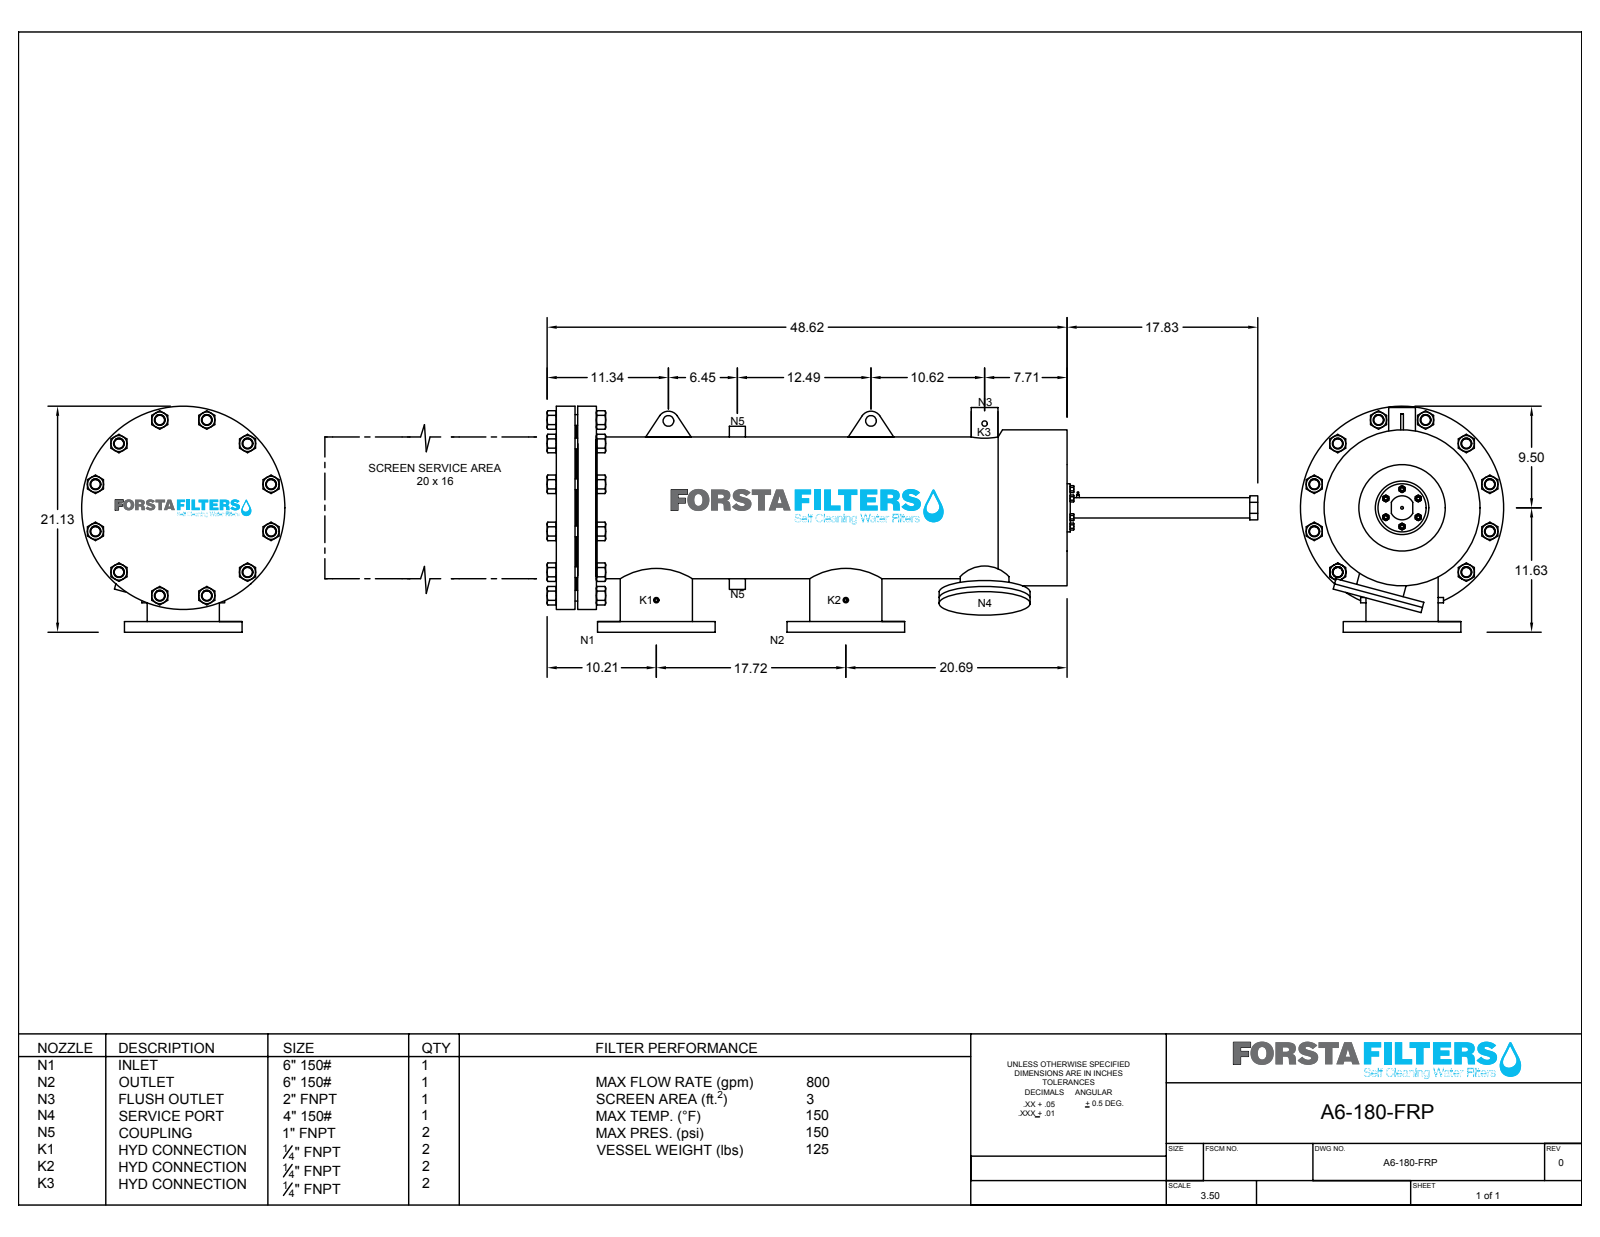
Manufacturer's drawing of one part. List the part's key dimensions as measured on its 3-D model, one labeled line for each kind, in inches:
Part name (STEP PRODUCT): A6-FRP-180
STEP written by: SolidWorks 2018 (CONFIG_CONTROL_DESIGN)
Units: inches
Bodies: 33 solids, 638 faces (306 planar, 328 cylindrical, 4 other)
Overall size (bounding box): 67.113 × 21.13 × 19
Volume: 1 571 in³ · Surface area: 7 748 in²
Round holes (diameter × count): ⌀0.75 ×16, ⌀0.88 ×16, ⌀1 ×15, ⌀0.25 ×4, ⌀0.375 ×4, ⌀0.375 ×2, ⌀4.106 ×2, ⌀5.996 ×2, ⌀1.51 ×1, ⌀2 ×1, ⌀12.858 ×1, ⌀14.187 ×1
Round bosses / shafts (diameter × count): ⌀0.35 ×6, ⌀0.644 ×3, ⌀11 ×2, ⌀9 ×2, ⌀6.39 ×2, ⌀4.5 ×2, ⌀19 ×1, ⌀14.581 ×1
Partial cylindrical surfaces — rounded edges, fillets, slot ends (radius × count): R1 ×2, R1.125 ×1
Main face-to-face distances: 2, 1.75, 0.25, 0.5, 1, 48.62, 46.87, 46.62, 3.75, 44.87
Hole centre spacings: 2.87, 3.75, 5.303, 6.929, 8.5, 8.777, 3.635, 12.02
